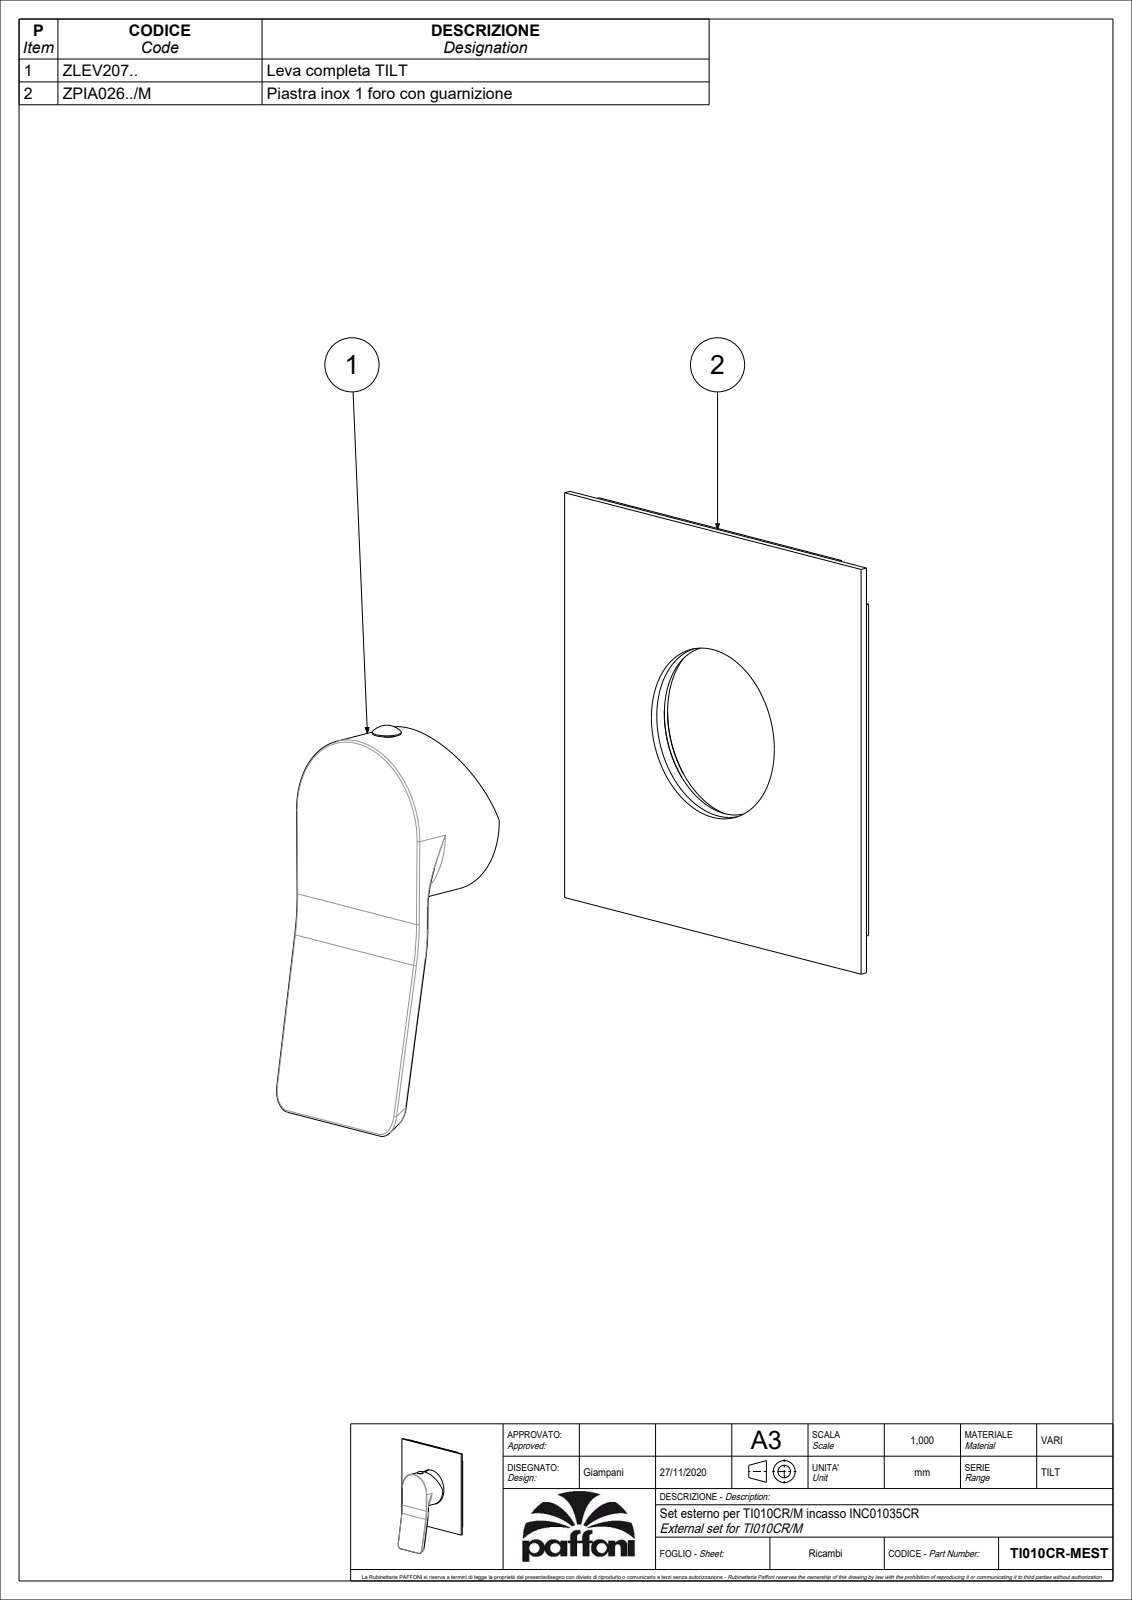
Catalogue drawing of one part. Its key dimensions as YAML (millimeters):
part_name: "TI010CR-MEST"
step_written_by: "CREO PARAMETRIC BY PTC INC, 2020044 (CONFIG_CONTROL_DESIGN)"
units: millimeters
bodies: {solids: 2, faces: 156, planar: 75, cylindrical: 44, other: 37}
overall_size: [134.58, 110, 48.45]
volume: 52780
surface_area: 43196
round_holes:
  - {diameter: 3, count: 1}
  - {diameter: 45.6, count: 1}
  - {diameter: 47.6, count: 1}
  - {diameter: 51.1, count: 1}
round_bosses_or_shafts:
  - {diameter: 54.6, count: 1}
  - {diameter: 45.5, count: 1}
  - {diameter: 7.6, count: 1}
  - {diameter: 5.5, count: 1}
  - {diameter: 5, count: 1}
partial_cylinders:
  - {radius: 0.5, count: 10}
  - {radius: 1.5, count: 2}
  - {radius: 5, count: 2}
  - {radius: 44.14, count: 1}
  - {radius: 63, count: 1}
face_to_face_distances: [2, 0.8, 2.8, 4.01, 32, 34.8, 34, 4, 30, 30.8]
